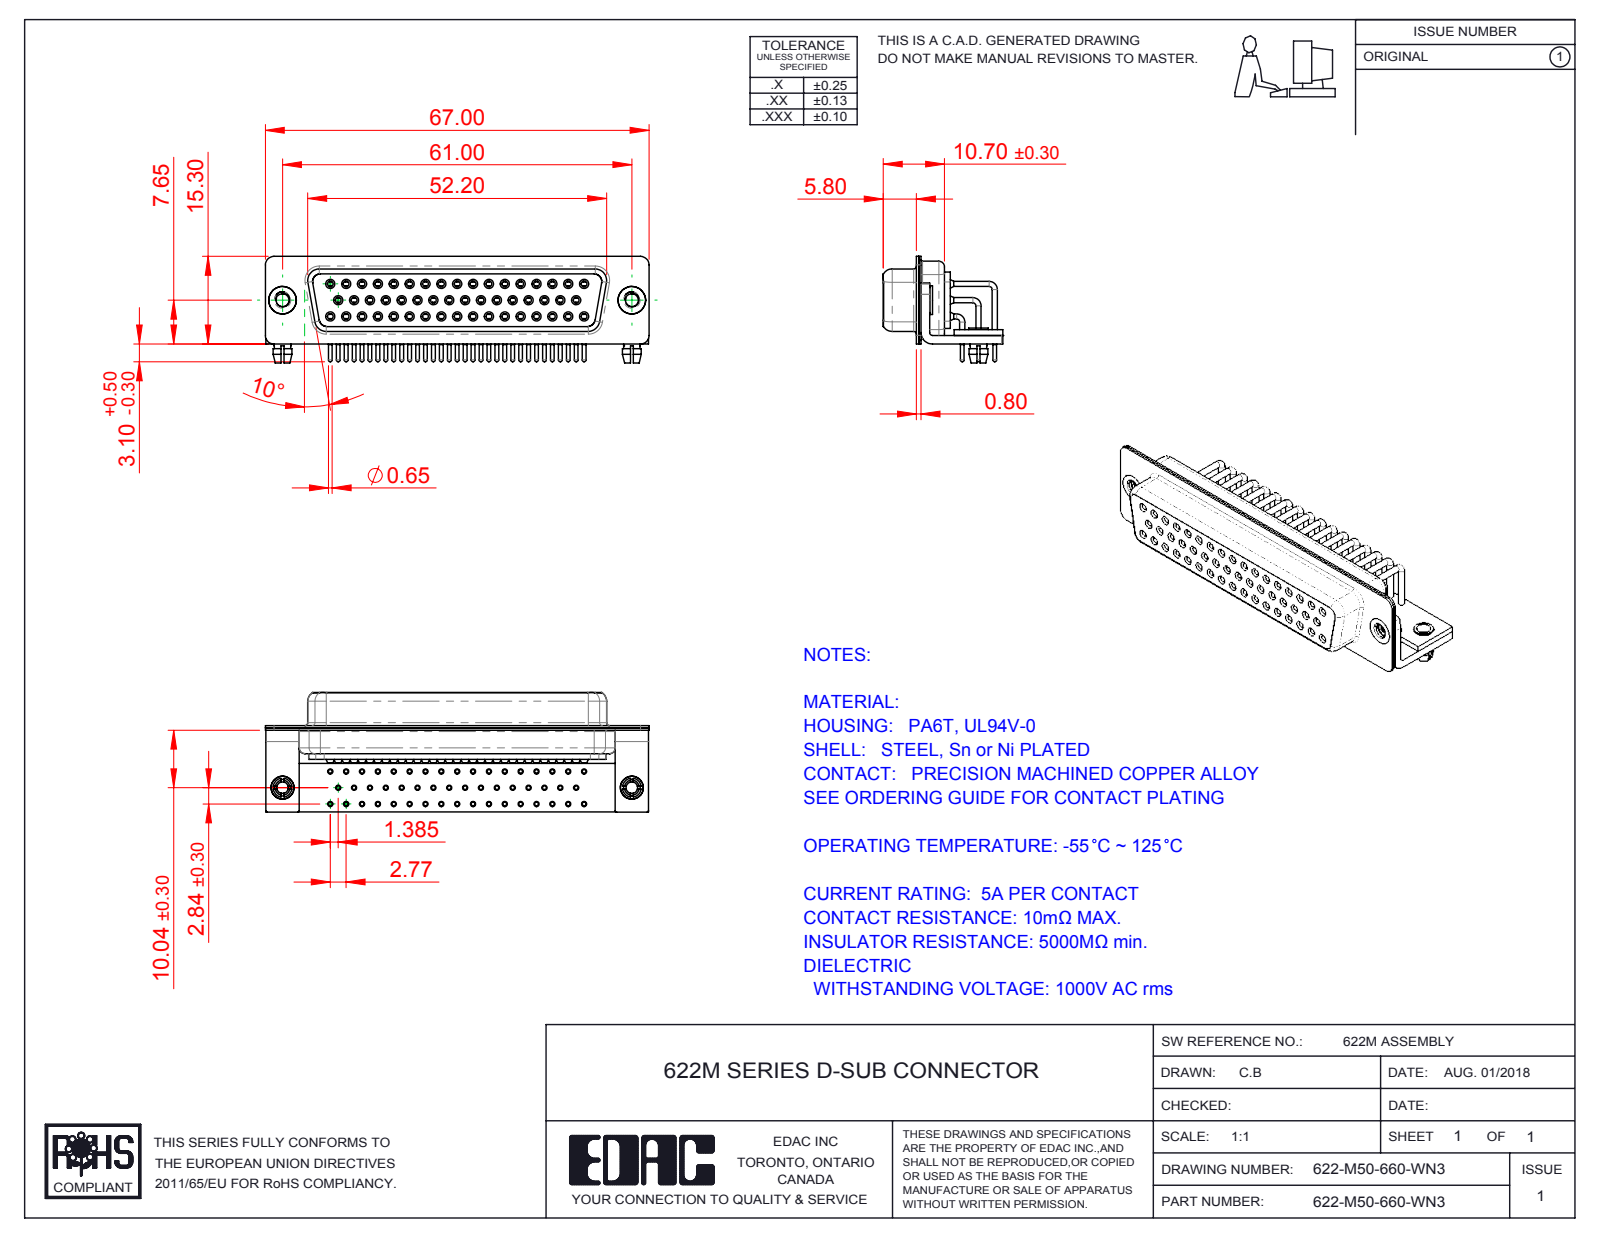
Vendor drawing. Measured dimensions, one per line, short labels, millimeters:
name: 622M Shell Front_50 Contacts; 622M Housing_50 Contacts; 622-M50-660-WN3; 622M Board Lock_50 Contacts (+7 more)
written by: SolidWorks 2016 (CONFIG_CONTROL_DESIGN)
unit: mm
bodies: 60 solids, 3171 faces (891 planar, 1441 cylindrical, 839 other)
size: 67 × 20.9 × 18.6
volume: 7 790 mm³; area: 18 357 mm²
holes: 52× ⌀2, 50× ⌀0.9, 50× ⌀1, 50× ⌀1.1, 50× ⌀1.7, 50× ⌀1.8, 2× ⌀2.26, 2× ⌀2.5, 2× ⌀3.2, 2× ⌀4, 2× ⌀4.8
bosses: 59× ⌀0.9, 50× ⌀1.6, 50× ⌀1.5, 50× ⌀0.65, 2× ⌀5, 2× ⌀4.9, 2× ⌀4, 2× ⌀3.4
rounds: 16× R0.25, 16× R1.5, 13× R2, 8× R1.35, 8× R1.6, 5× R0.5, 4× R0.6, 4× R0.65
face distances: 0.4, 1, 2.2, 0.85, 1.35, 11.85, 12.25, 5.8, 5.9, 0.8
hole spacings: 2.77, 3.16, 5.54, 8.31, 11.08, 13.85, 16.62, 19.39
